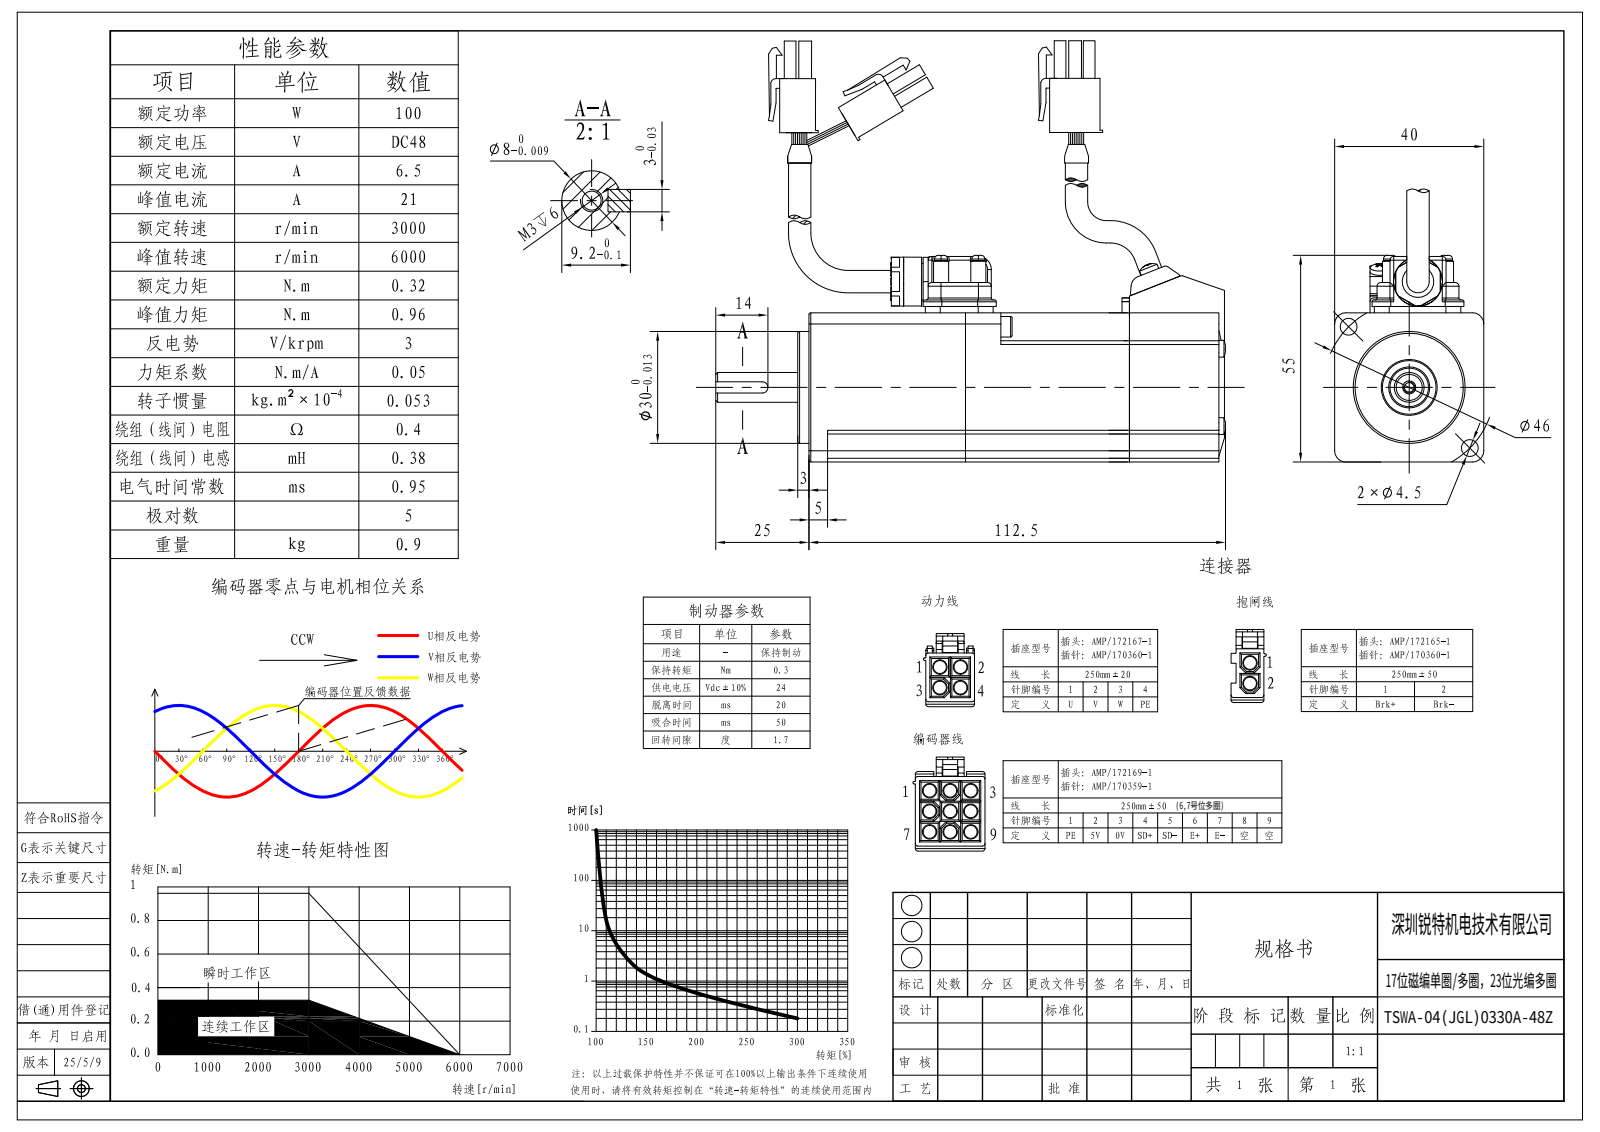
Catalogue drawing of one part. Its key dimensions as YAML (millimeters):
step_written_by: "SolidWorks 2018 (CONFIG_CONTROL_DESIGN)"
units: millimeters
bodies: {solids: 0, faces: 2117, planar: 181, cylindrical: 146, other: 1790}
overall_size: [137.57, 53.71, 41]
round_holes:
  - {diameter: 2.05, count: 4}
  - {diameter: 2.5, count: 4}
  - {diameter: 2, count: 2}
  - {diameter: 3.5, count: 2}
  - {diameter: 4.5, count: 2}
  - {diameter: 6.3, count: 1}
  - {diameter: 8, count: 1}
  - {diameter: 10, count: 1}
  - {diameter: 12, count: 1}
  - {diameter: 15, count: 1}
  - {diameter: 16.33, count: 1}
  - {diameter: 20, count: 1}
round_bosses_or_shafts:
  - {diameter: 5, count: 4}
  - {diameter: 5.5, count: 2}
  - {diameter: 3, count: 2}
  - {diameter: 30, count: 1}
  - {diameter: 12.67, count: 1}
  - {diameter: 9, count: 1}
  - {diameter: 8.9, count: 1}
  - {diameter: 8, count: 1}
partial_cylinders:
  - {radius: 0.3, count: 16}
  - {radius: 1, count: 16}
  - {radius: 1.25, count: 6}
  - {radius: 4.5, count: 6}
  - {radius: 3, count: 5}
  - {radius: 0.5, count: 4}
  - {radius: 2, count: 4}
  - {radius: 3.25, count: 2}
face_to_face_distances: [40, 2, 7.5, 1.5, 32.5, 0.5, 70, 68.5, 110.5, 110]
hole_center_spacings: [8, 20.75, 16, 23, 6.12, 6.13, 26.68, 26.69]
